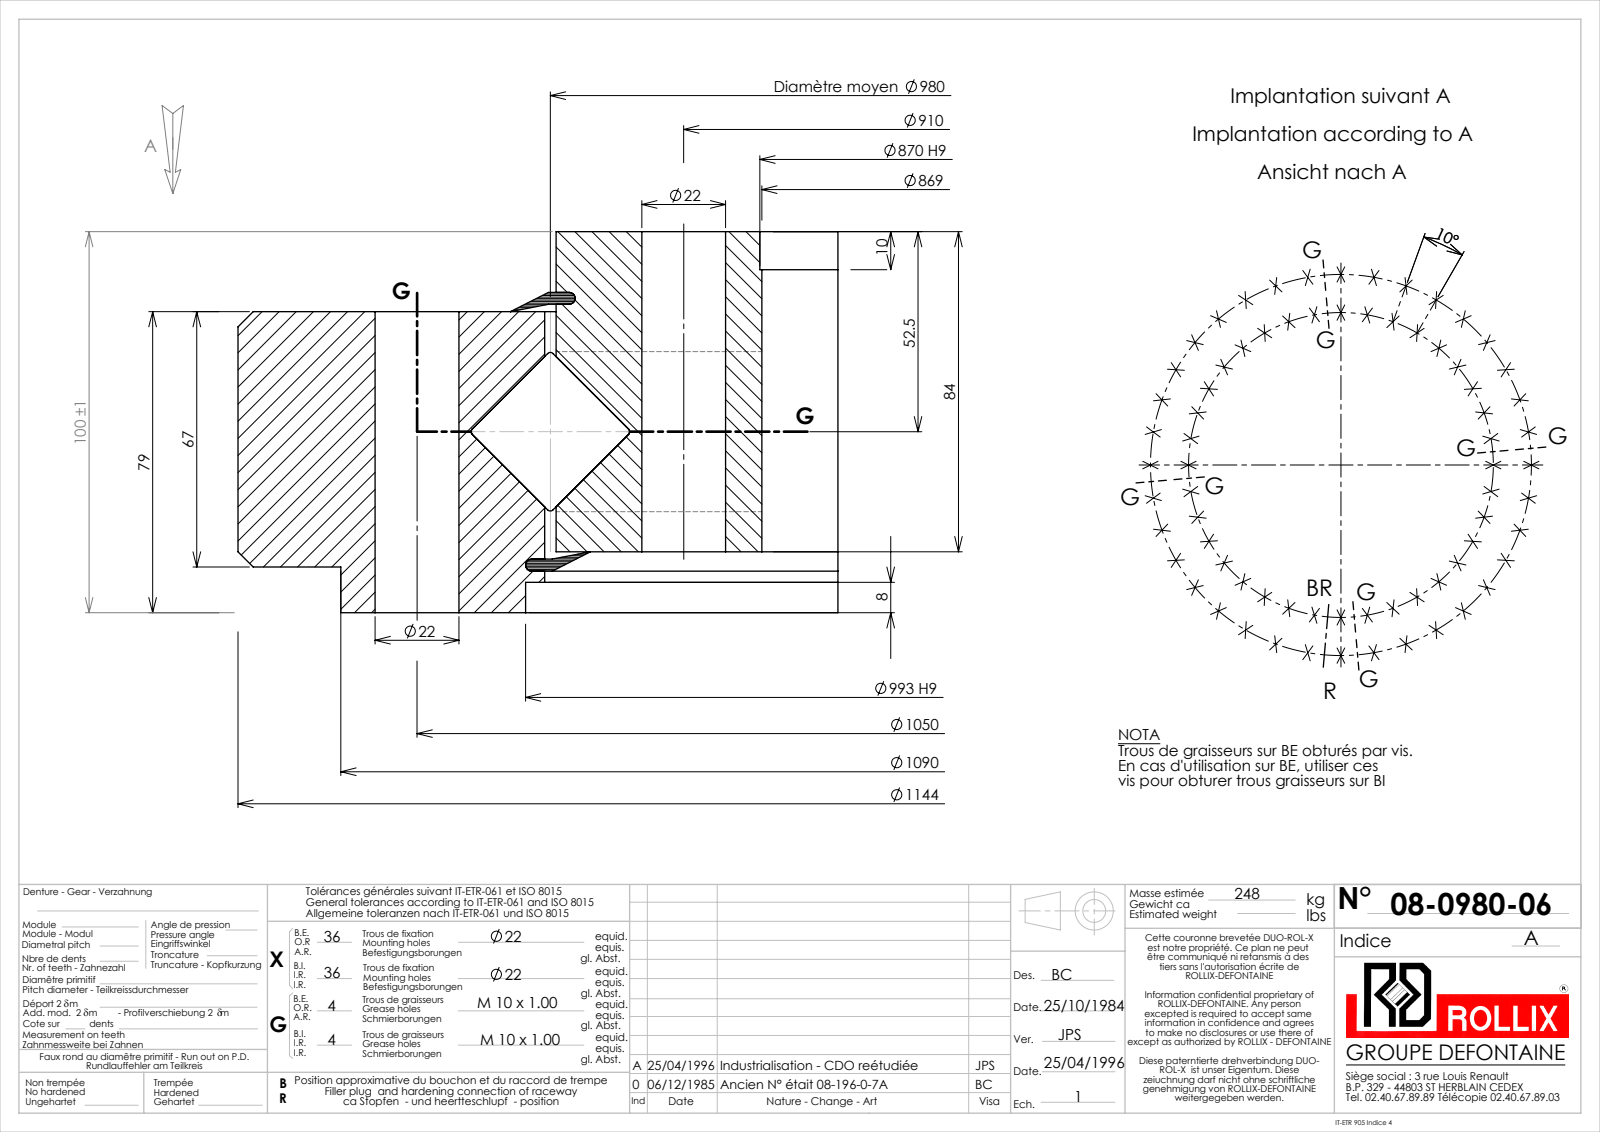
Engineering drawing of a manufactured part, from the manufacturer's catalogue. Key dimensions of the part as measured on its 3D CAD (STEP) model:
Part name (STEP PRODUCT): 08-0980-06
STEP written by: SolidWorks 2016 (CONFIG_CONTROL_DESIGN)
Units: millimetres
Bodies: 5 solids, 257 faces (17 planar, 184 cylindrical, 56 other)
Overall size (bounding box): 1144 × 1144 × 100
Volume: 28 590 000 mm³ · Surface area: 2 588 000 mm²
Round holes (diameter × count): ⌀22 ×72, ⌀9 ×8, ⌀869 ×1, ⌀870 ×1, ⌀983 ×1, ⌀993 ×1
Round bosses / shafts (diameter × count): ⌀1144 ×1, ⌀1090 ×1, ⌀977 ×1, ⌀30 ×1
Main face-to-face distances: 79, 16, 63, 100, 84, 21, 4, 12, 67, 88
Hole centre spacings: 182.33, 742.46, 525, 271.76, 443.75, 1014.22, 91.51, 674.92
